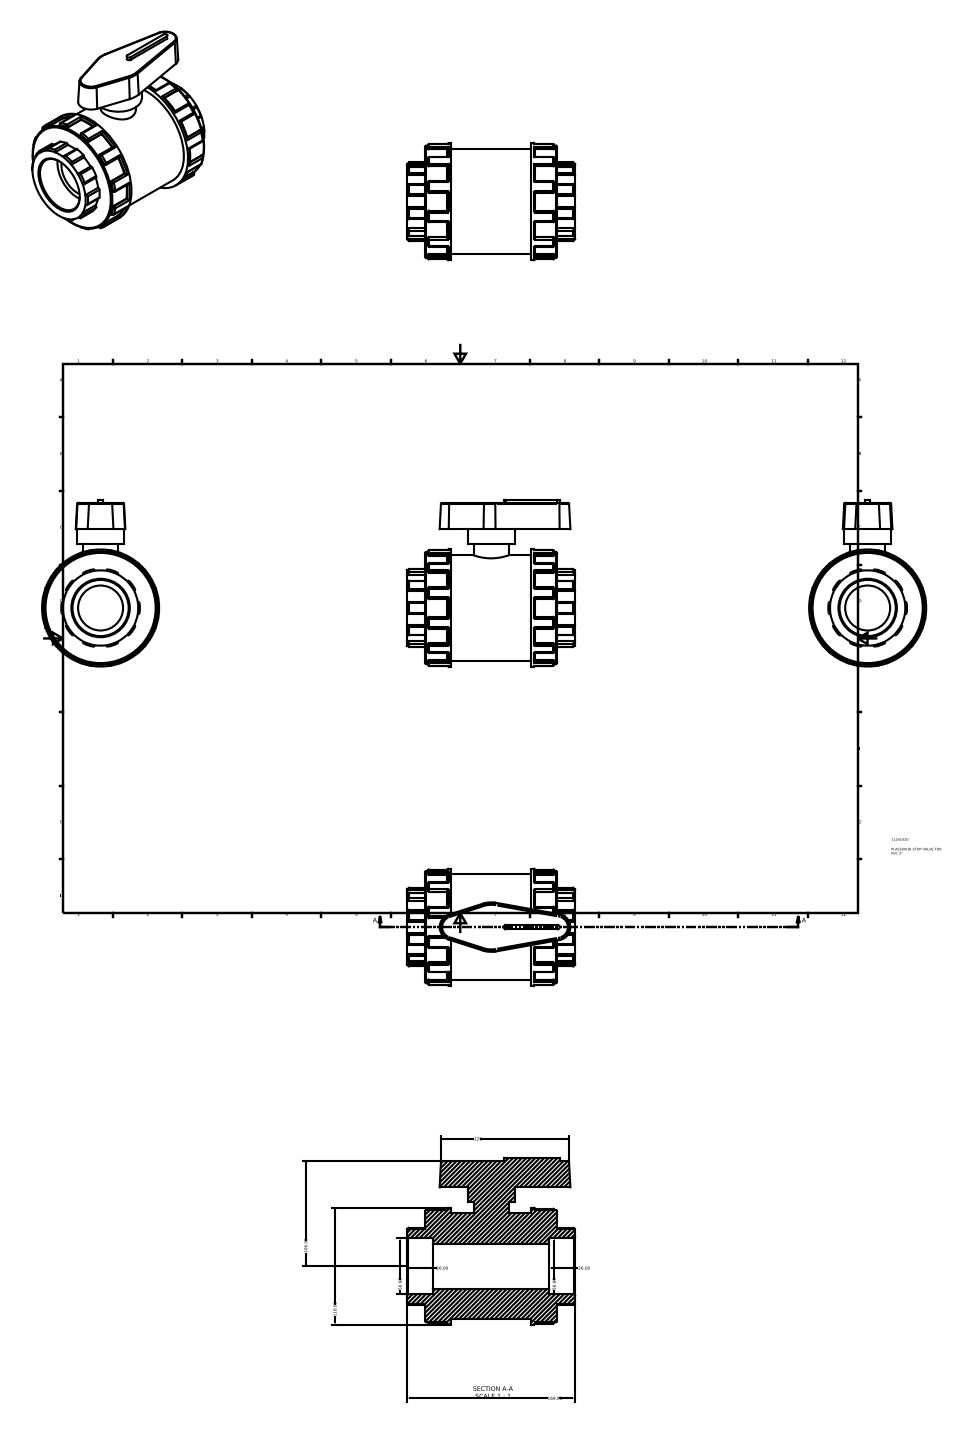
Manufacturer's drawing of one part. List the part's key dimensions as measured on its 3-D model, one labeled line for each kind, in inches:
Part name (STEP PRODUCT): 11241020
STEP written by: Autodesk Inventor 2015 (AUTOMOTIVE_DESIGN)
Units: inches
Bodies: 1 solid, 434 faces (114 planar, 192 cylindrical, 128 other)
Overall size (bounding box): 6.654 × 6.621 × 4.646
Volume: 77.26 in³ · Surface area: 190.4 in²
Round holes (diameter × count): ⌀1.784 ×1, ⌀2.231 ×1
Round bosses / shafts (diameter × count): ⌀4.646 ×1, ⌀4.46 ×1, ⌀4.181 ×1, ⌀1.858 ×1, ⌀1.394 ×1
Partial cylindrical surfaces — rounded edges, fillets, slot ends (radius × count): R0.067 ×84, R0.044 ×4, R0.093 ×2, R1.494 ×1, R1.561 ×1
Main face-to-face distances: 1.024, 0.717, 4.913, 5.22, 4.197, 1.74, 5.937, 1.043, 3.173, 5.63
